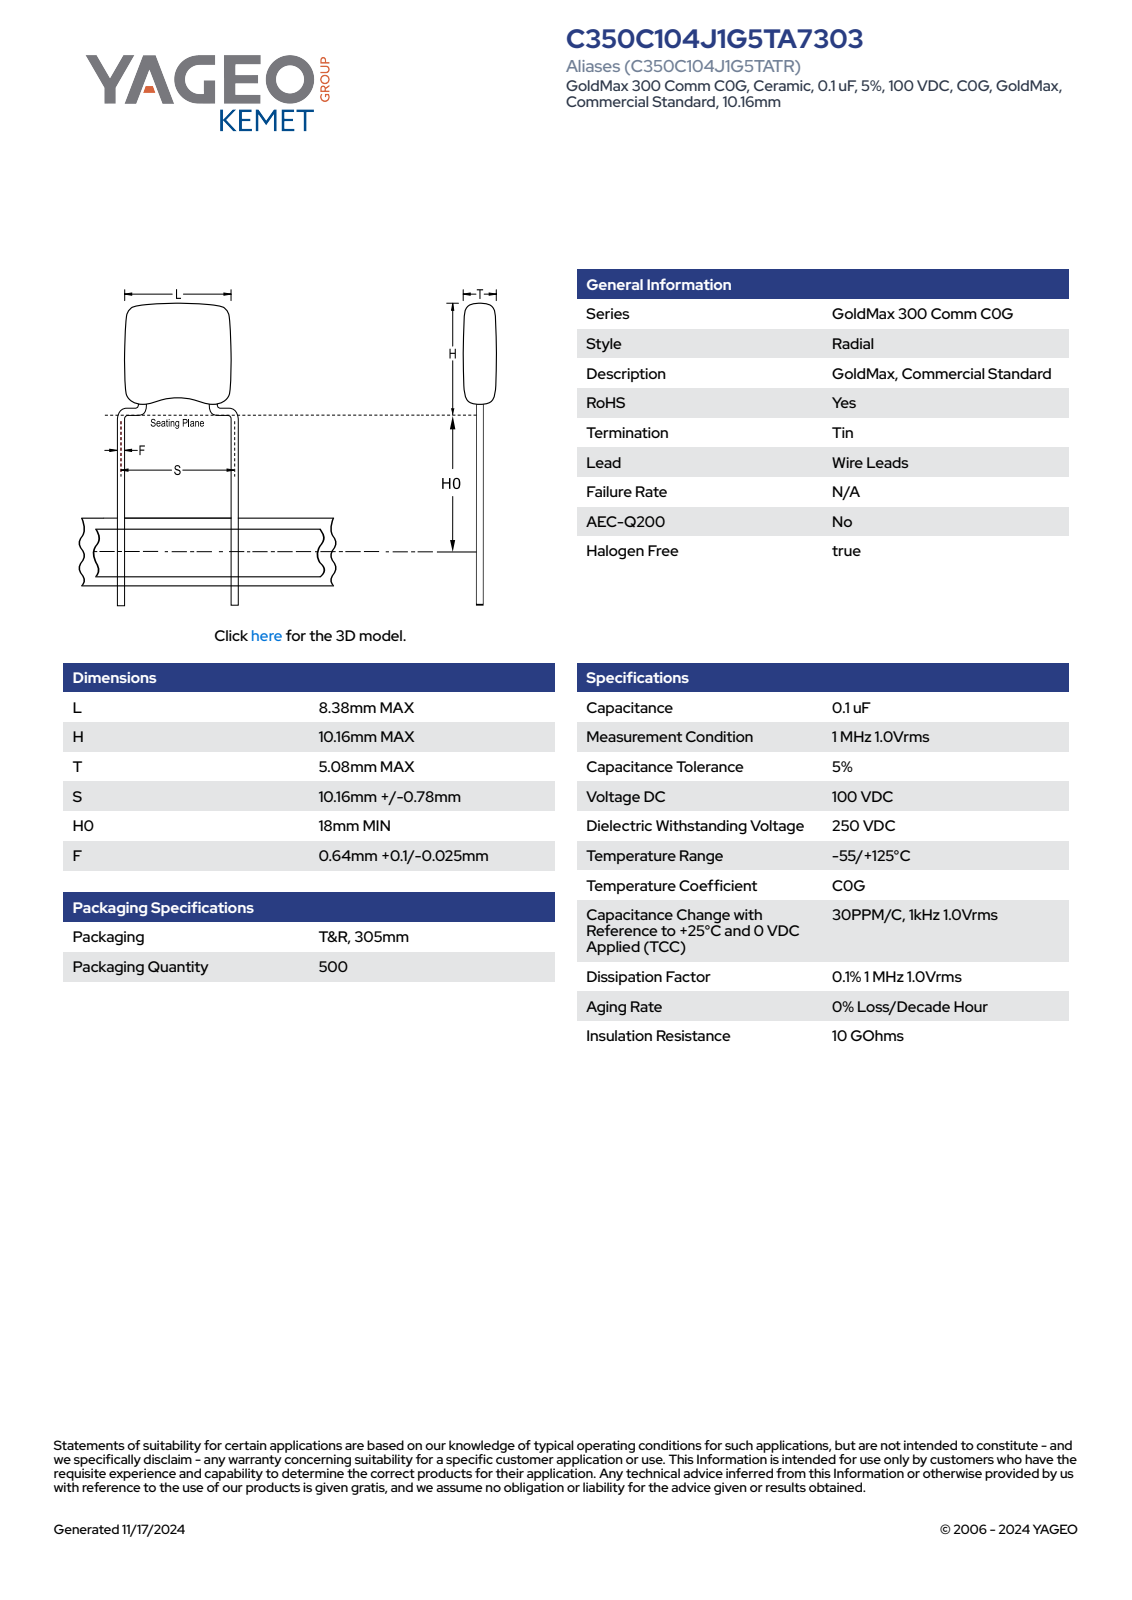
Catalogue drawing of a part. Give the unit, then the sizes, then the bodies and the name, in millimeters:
Units: millimetres
Overall size (bounding box): 28.16 × 10.8 × 5.08
Round bosses / shafts (diameter × count): ⌀0.64 ×2
Partial cylindrical surfaces — rounded edges, fillets, slot ends (radius × count): R1 ×10
Main face-to-face distances: 5.08, 8.38, 7.94, 4.29, 3.65, 3.58, 0.71, 4.36, 0.72, 0.8
Volume: 336 mm³ · Surface area: 352 mm²
Bodies: 4 solids, 99 faces (67 planar, 14 cylindrical, 18 other)
Part name (STEP PRODUCT): CCR_SB_8.38X10.16_L8.38H10.16T5.08S10.16H018F0.64
STEP written by: SolidWorks 2014 (AUTOMOTIVE_DESIGN)
